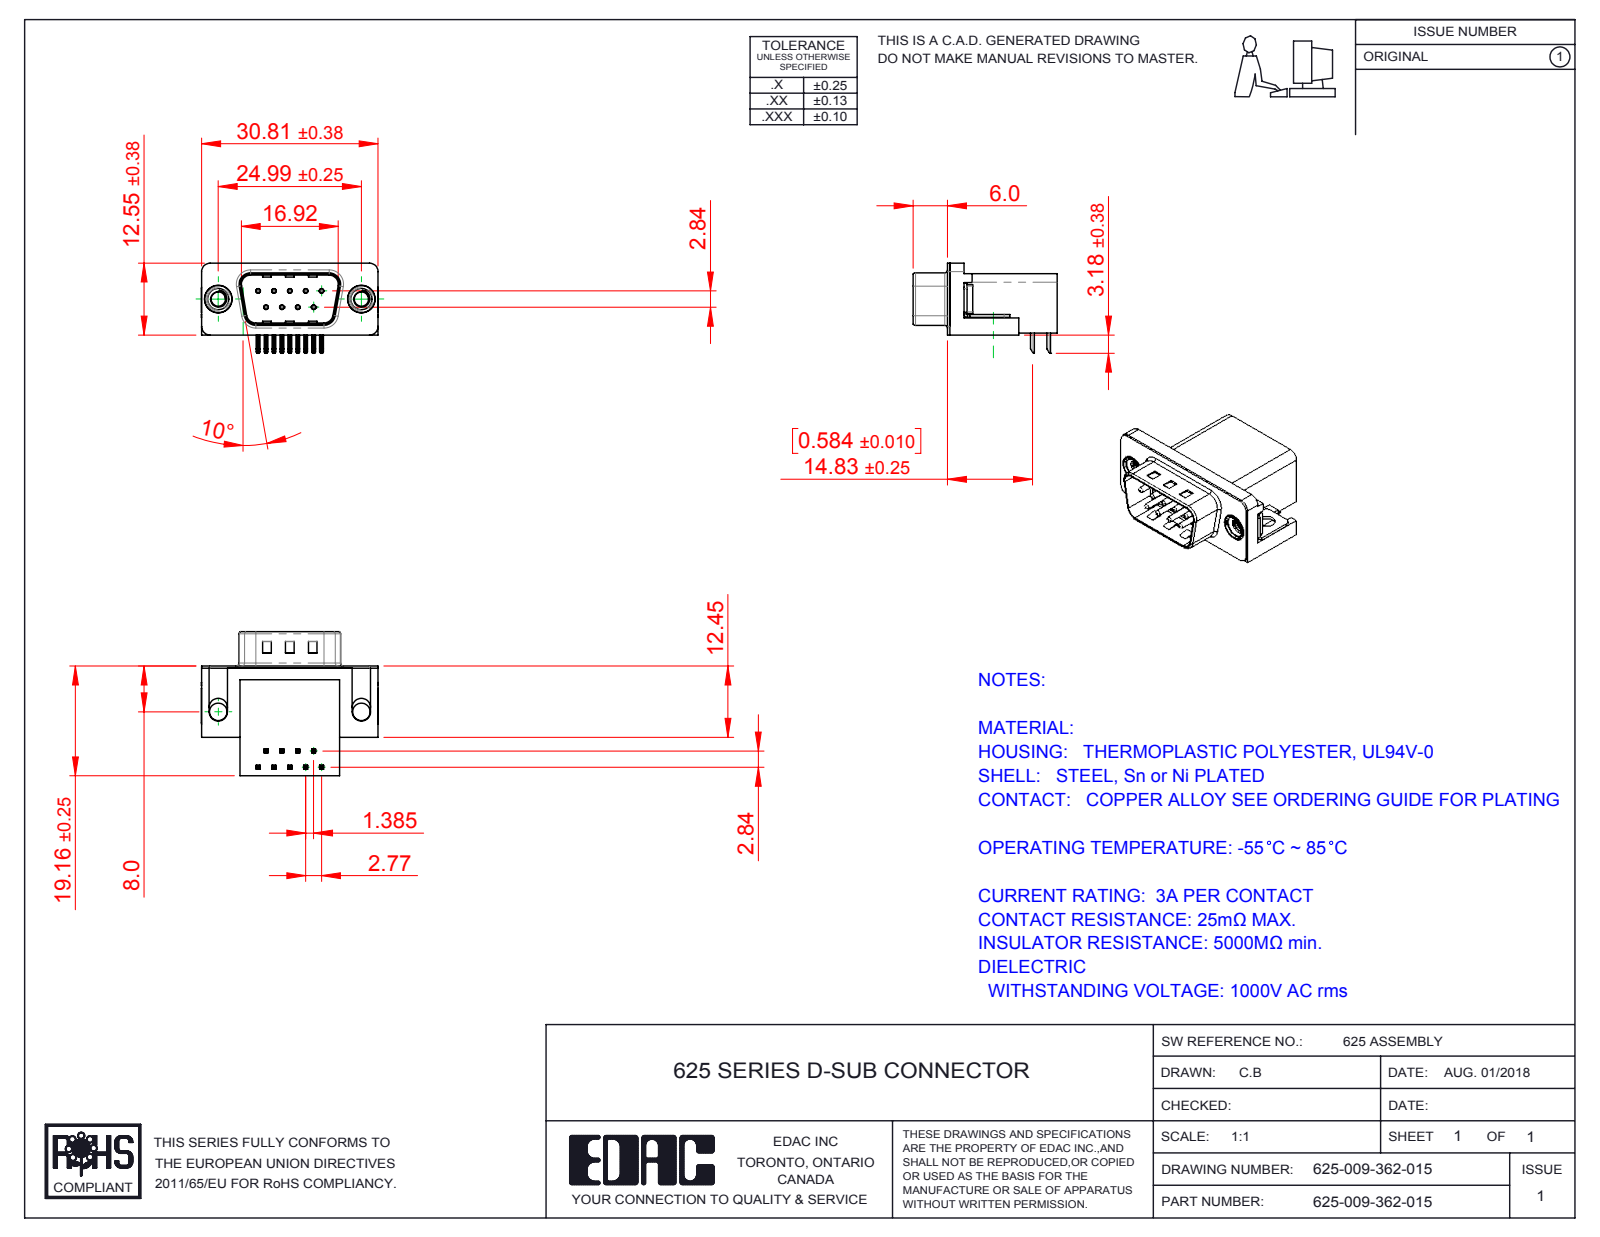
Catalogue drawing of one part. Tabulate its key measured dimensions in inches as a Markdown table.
| quantity | value |
| --- | --- |
| part name | 625 Contact Top; 625-009-362-015; 625 Contact Bottom; 625 Shell_9 Socket (+3 more) |
| STEP written by | SolidWorks 2016 (CONFIG_CONTROL_DESIGN) |
| units | inches |
| bodies | 15 solids, 993 faces (573 planar, 321 cylindrical, 99 other) |
| overall size | 1.216 × 0.991 × 0.619 |
| volume | 0.273 in³ |
| surface area | 7.66 in² |
| round holes (diameter × count) | 0.014 × 9, 0.031 × 9, 0.098 × 2, 0.12 × 2, 0.157 × 2, 0.189 × 2, 0.197 × 2 |
| round bosses / shafts (diameter × count) | 0.03 × 9, 0.193 × 2, 0.187 × 2, 0.154 × 2 |
| partial cylindrical surfaces (radius × count) | 0.01 × 44, 0.005 × 18, 0.039 × 16, 0.02 × 9, 0.059 × 8, 0.063 × 8, 0.035 × 4, 0.079 × 4 |
| main face-to-face distances | 0.016, 0.407, 0.739, 0.754, 0.114, 0.64, 0.098, 0.02, 0.014, 0.421 |
| hole center spacings | 0.124, 0.109, 0.218, 0.198, 0.198, 0.327, 0.294, 0.295 |
